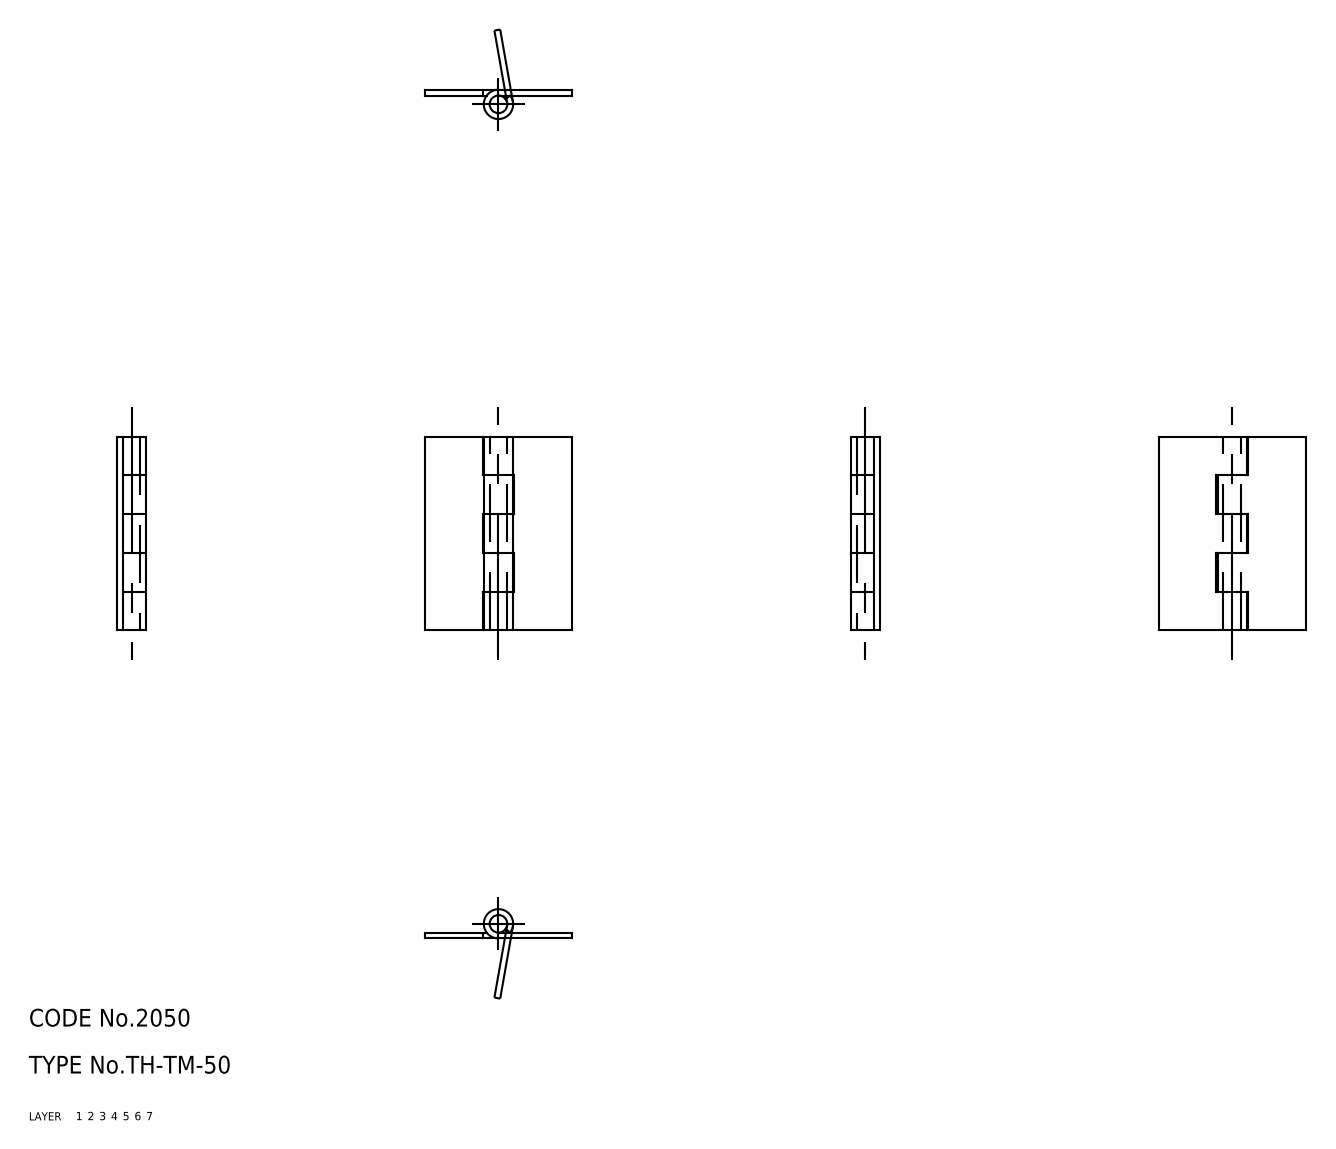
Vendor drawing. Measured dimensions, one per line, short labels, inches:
name: hinge piece_B; hinge piece_A; shaft; TH_TM_50_23888_36
written by: CADfix (AUTOMOTIVE_DESIGN)
unit: in
bodies: 3 solids, 42 faces (0 planar, 0 cylindrical, 42 other)
size: 1.299 × 0.984 × 0.197
volume: 0.081 in³; area: 4.349 in²
